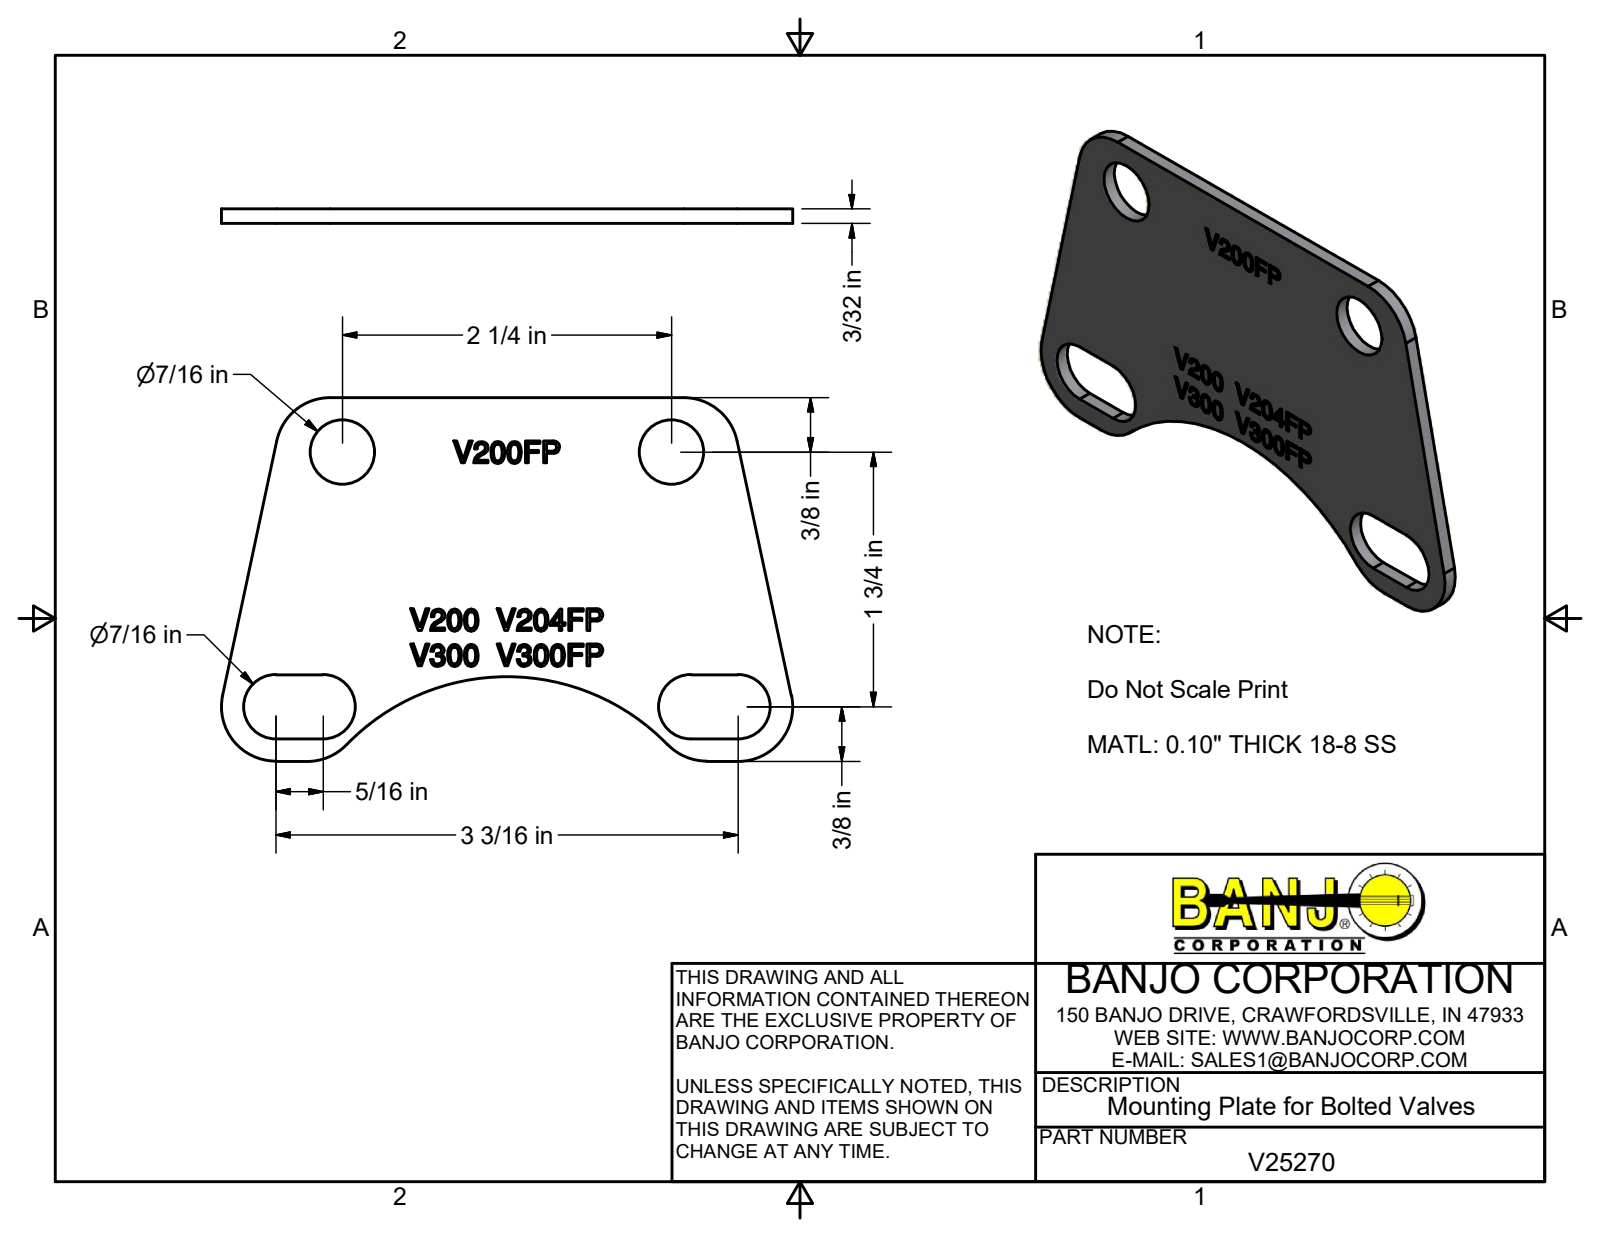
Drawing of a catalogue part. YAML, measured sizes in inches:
part_name: "V25270"
step_written_by: "Autodesk Inventor 2017 (AUTOMOTIVE_DESIGN)"
units: inches
bodies: {solids: 1, faces: 352, planar: 179, cylindrical: 13, other: 160}
overall_size: [3.927, 2.5, 0.1]
volume: 0.69
surface_area: 15.88
round_holes:
  - {diameter: 0.44, count: 2}
partial_cylinders:
  - {radius: 0.375, count: 6}
  - {radius: 0.22, count: 4}
  - {radius: 1.536, count: 1}
face_to_face_distances: [0.1, 0.09, 1.905, 2.345, 0.44, 2.5, 0.595, 0.155, 0.126, 0.019]
hole_center_spacings: [2.263]
